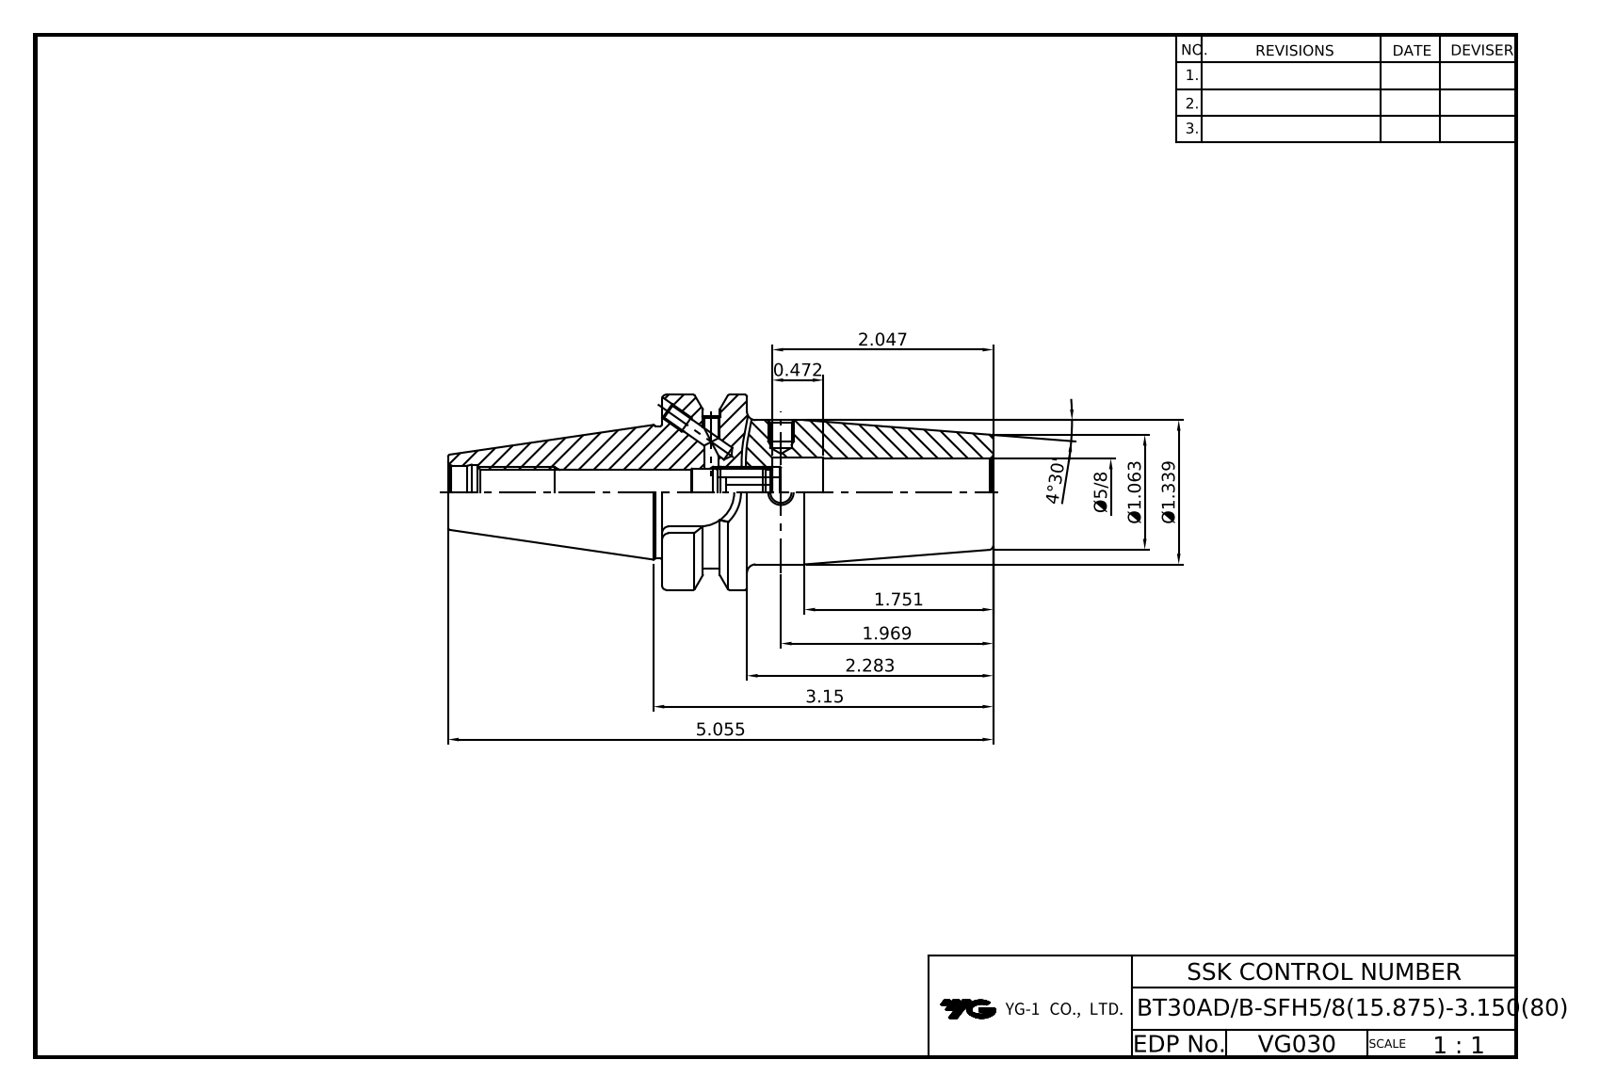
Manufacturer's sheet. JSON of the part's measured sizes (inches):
{"part_name": "LO-BT30-SFH15.875-3.15", "step_written_by": "Autodesk Inventor 2025 (AUTOMOTIVE_DESIGN)", "units": "inches", "bodies": {"solids": 1, "faces": 50, "planar": 17, "cylindrical": 15, "other": 18}, "overall_size": [5.055, 1.811, 1.811], "volume_in3": 4.931, "surface_area_in2": 31.62, "round_holes": [[0.398, 1], [0.43, 1], [0.492, 1], [0.516, 1], [0.625, 1], [0.649, 1]], "round_bosses_or_shafts": [[1.811, 1], [1.339, 1], [1.228, 1]], "partial_cylinders_radius": [[0.317, 1], [0.74, 1]], "face_to_face_distances": [0.787, 1.283, 3.071, 2.283, 1.024, 0.236, 2.047, 0.634, 1.984, 2.772]}
